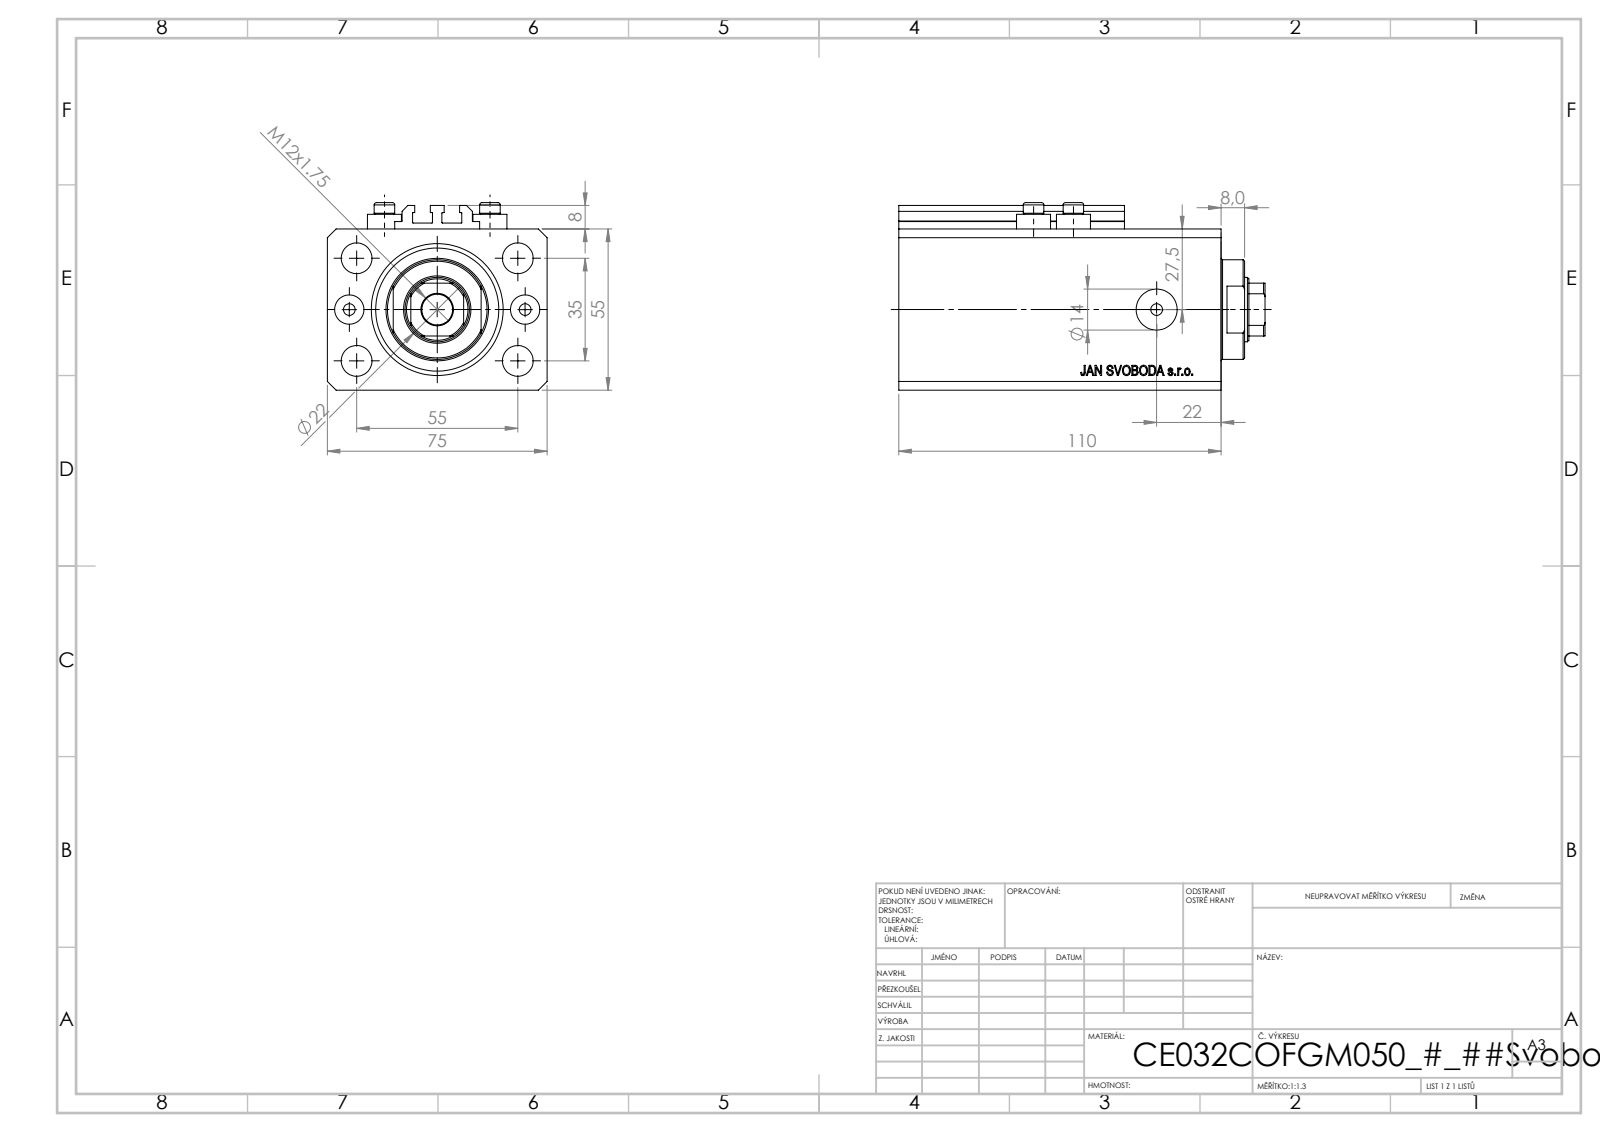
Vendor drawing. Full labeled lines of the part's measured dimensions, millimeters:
Part name (STEP PRODUCT): ALLEN BOLT V250CE; V250CE_VC_C; V250CE_C_VCP; V250CE_C_Body
STEP written by: SolidWorks 2019 (CONFIG_CONTROL_DESIGN)
Units: millimetres
Bodies: 8 solids, 1034 faces (504 planar, 86 cylindrical, 444 other)
Overall size (bounding box): 125 × 75 × 64
Volume: 408 931 mm³ · Surface area: 91 117 mm²
Round holes (diameter × count): ⌀4 ×8, ⌀10.5 ×5, ⌀10 ×2, ⌀14 ×2, ⌀22 ×1, ⌀32 ×1, ⌀45 ×1
Round bosses / shafts (diameter × count): ⌀11.6 ×4, ⌀7 ×4, ⌀34 ×1
Partial cylindrical surfaces — rounded edges, fillets, slot ends (radius × count): R0.2 ×10, R10.5 ×1
Main face-to-face distances: 55, 75, 110, 15, 95, 9.9, 85.1, 100.1, 3, 8
Hole centre spacings: 17.68, 32.6, 60.1, 13.6, 30, 35, 36, 38.48
